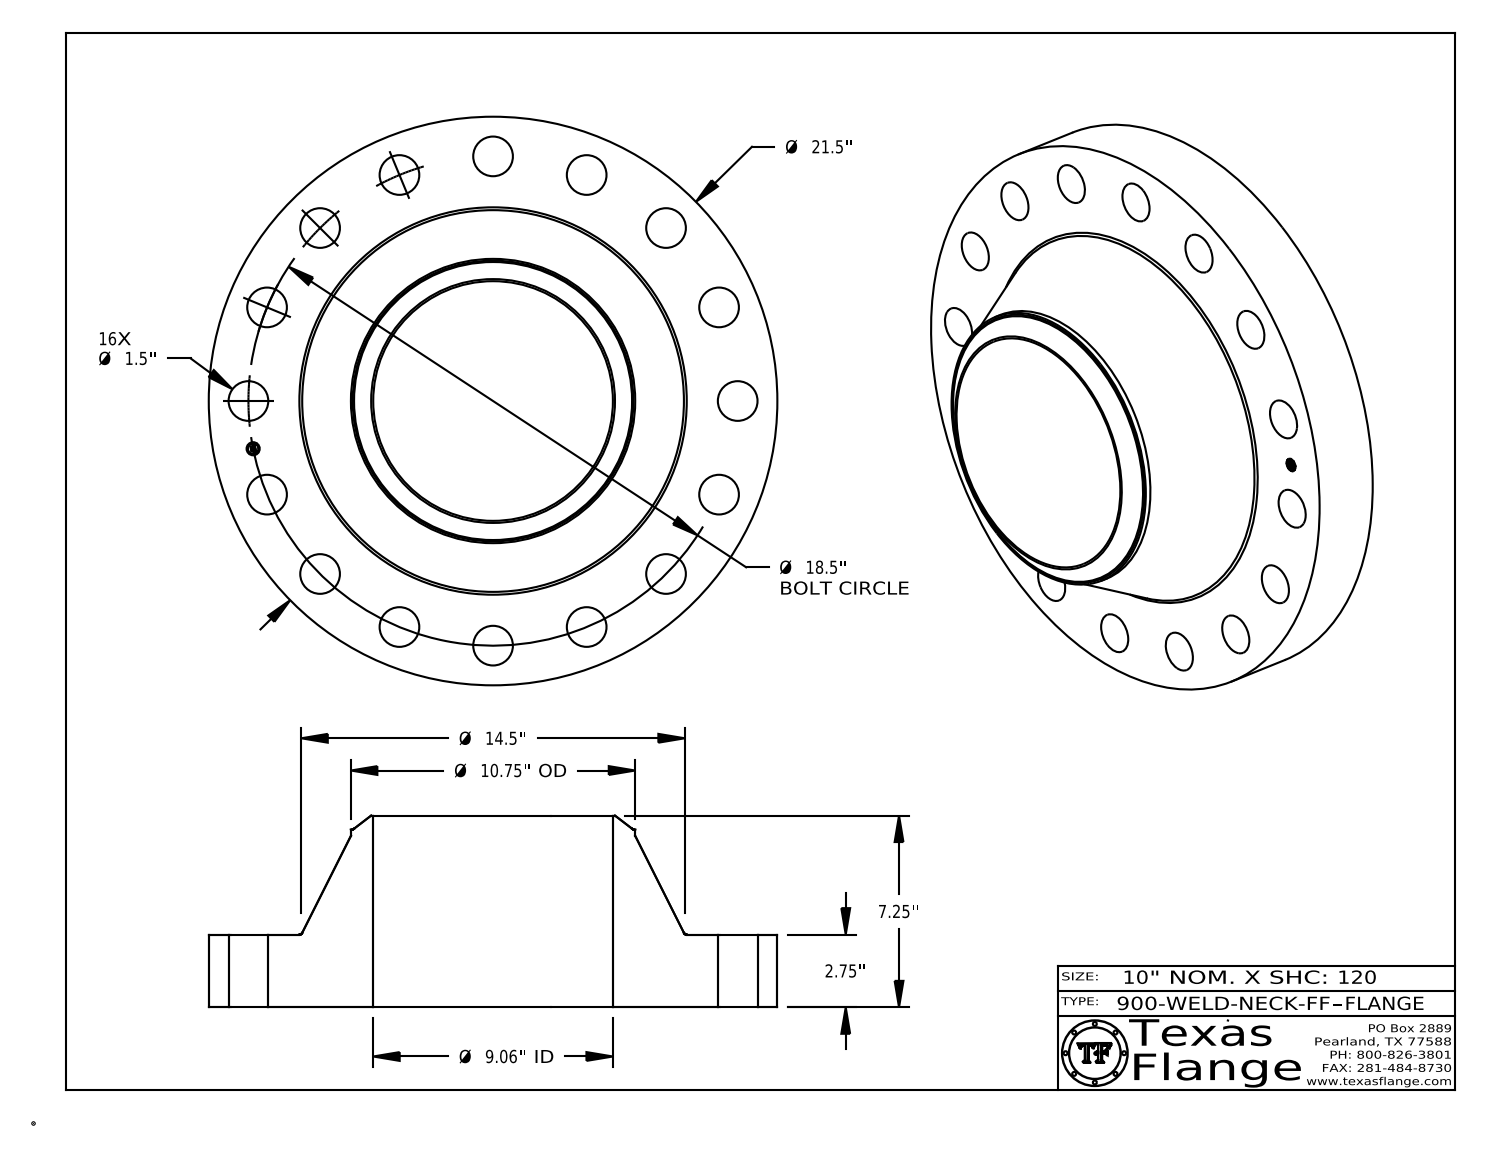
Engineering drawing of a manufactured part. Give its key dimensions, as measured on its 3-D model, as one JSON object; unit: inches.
{"part_name": "900-WELD-NECK-FF", "step_written_by": "CATIA V5 STEP AP214 (AUTOMOTIVE_DESIGN)", "units": "inches", "bodies": {"solids": 1, "faces": 436, "planar": 368, "cylindrical": 58, "other": 10}, "overall_size": [21.5, 21.5, 7.25], "volume_in3": 986.3, "surface_area_in2": 1244, "round_holes": [[1.5, 16], [0.495, 1], [9.062, 1]], "round_bosses_or_shafts": [[0.03, 8], [21.5, 1], [10.75, 1], [0.39, 1]], "face_to_face_distances": [2.75, 7.25, 4.5, 2.735, 0.015, 4.515, 0.148, 0.145, 0.027, 0.096], "hole_center_spacings": [15.382, 7.08, 9.25, 13.081, 3.609, 3.609, 10.278, 10.278]}
